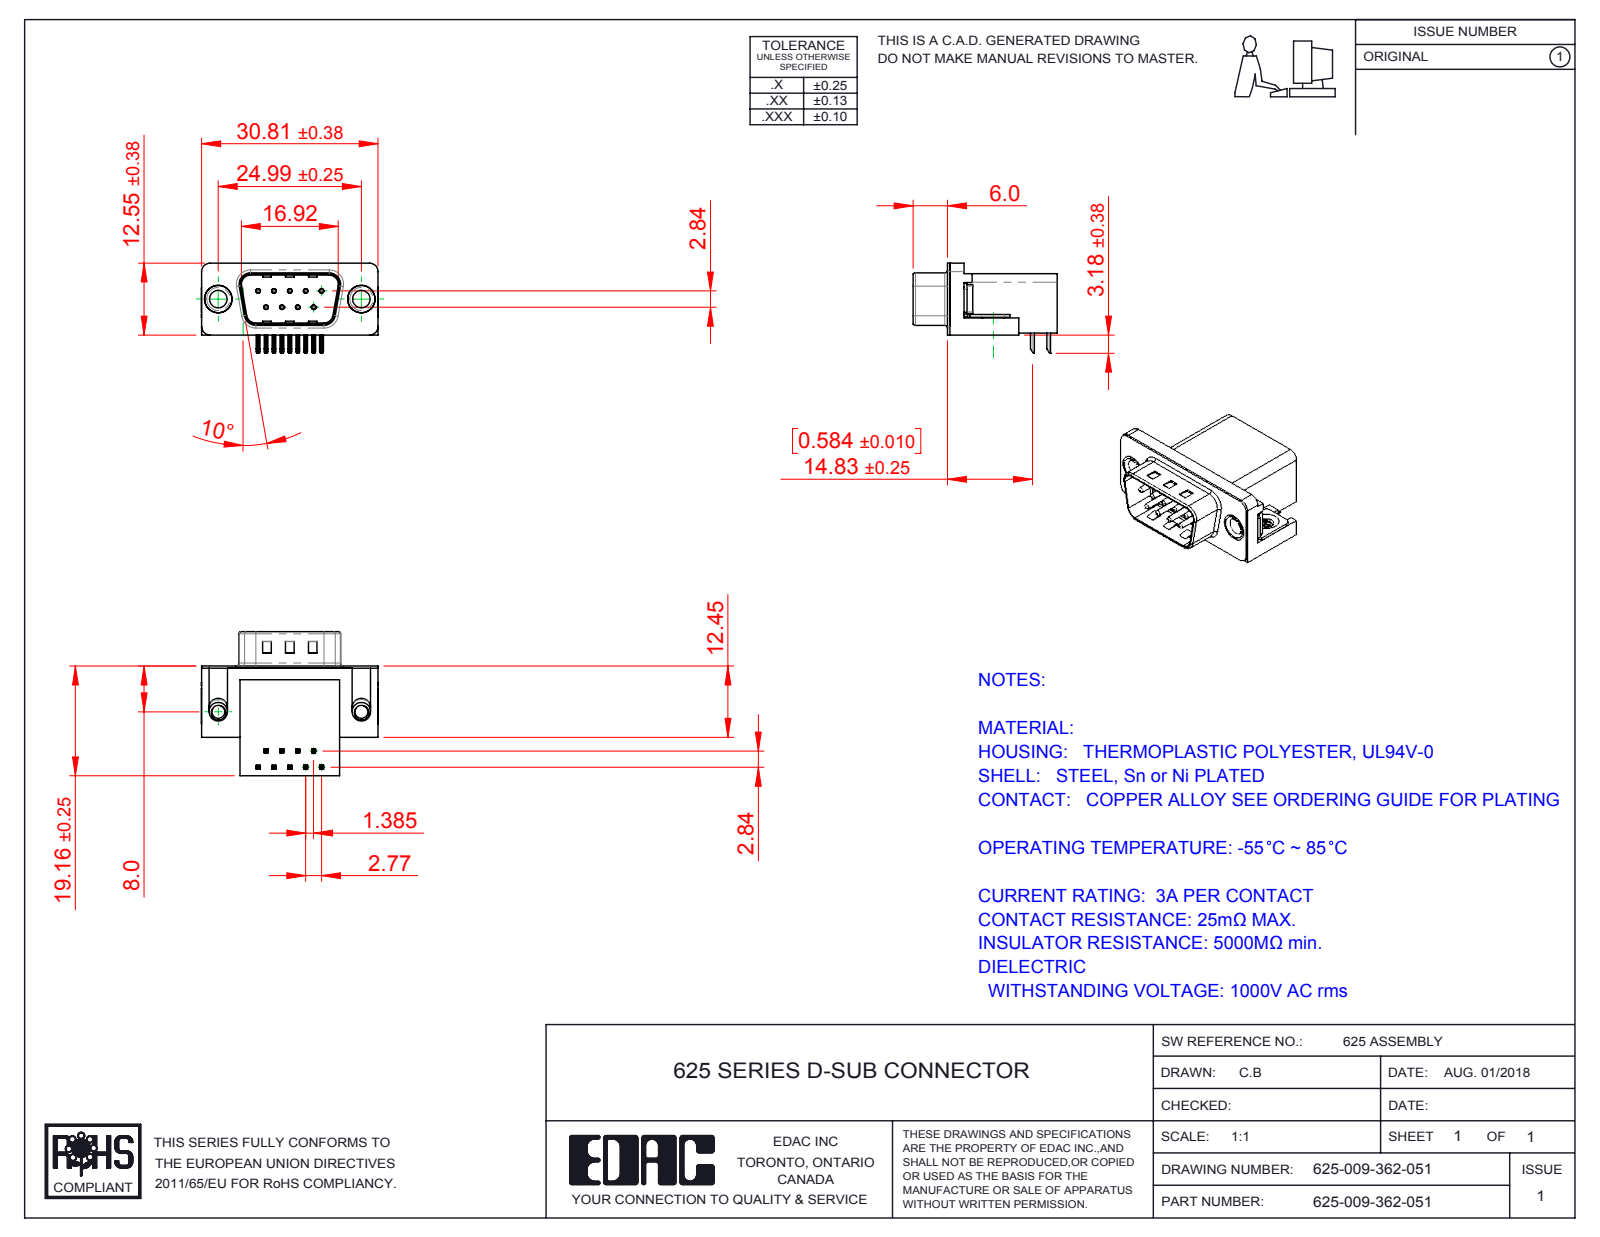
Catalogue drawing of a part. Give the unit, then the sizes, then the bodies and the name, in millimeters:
Units: millimetres
Overall size (bounding box): 30.89 × 25.16 × 15.73
Round holes (diameter × count): ⌀0.35 ×9, ⌀0.8 ×9, ⌀2.26 ×2, ⌀3.05 ×2, ⌀4 ×2, ⌀4.8 ×2, ⌀5 ×2
Round bosses / shafts (diameter × count): ⌀0.75 ×9, ⌀4.9 ×2, ⌀4.75 ×2, ⌀3.85 ×2, ⌀3.26 ×2
Partial cylindrical surfaces — rounded edges, fillets, slot ends (radius × count): R0.25 ×44, R0.12 ×18, R1 ×16, R0.5 ×9, R1.5 ×8, R1.6 ×8, R0.9 ×4, R2 ×4
Main face-to-face distances: 0.4, 10.34, 18.76, 19.16, 2.9, 16.26, 2.5, 0.35, 10.69, 6.7
Hole centre spacings: 3.16, 2.77, 5.54, 5.03, 5.04, 8.31, 7.48, 7.49
Volume: 4 474 mm³ · Surface area: 5 007 mm²
Bodies: 15 solids, 985 faces (575 planar, 311 cylindrical, 99 other)
Part name (STEP PRODUCT): 625 Thru Hole Rivet; 625-009-362-051; 625 Contact Top; 625 Shell_9 Socket (+3 more)
STEP written by: SolidWorks 2016 (CONFIG_CONTROL_DESIGN)
